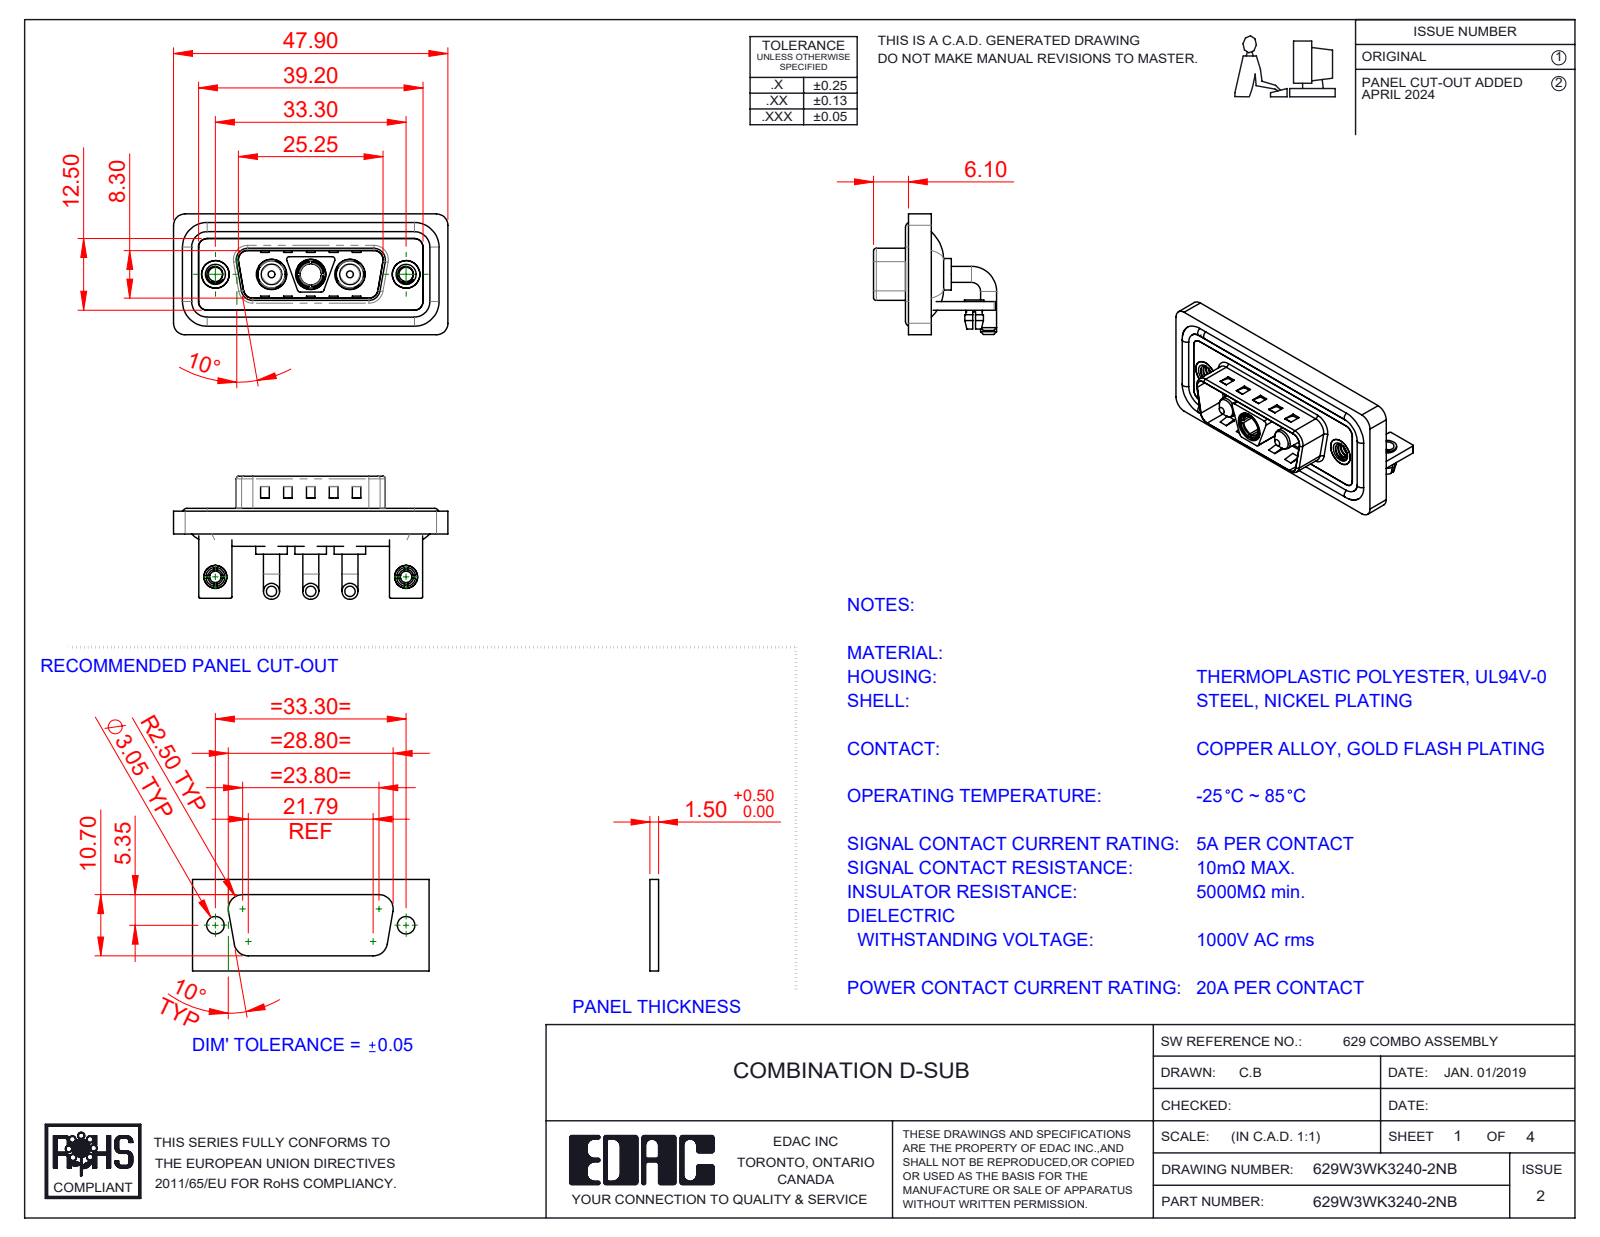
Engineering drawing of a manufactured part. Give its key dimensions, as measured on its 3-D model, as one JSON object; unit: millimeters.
{"part_name": "629Combo Board Lock; Power Pin_20A RA; Power Socket_20A RA; 629Combo Shell Rear_15 Contacts (+6 more)", "step_written_by": "SolidWorks 2023 (CONFIG_CONTROL_DESIGN)", "units": "millimeters", "bodies": {"solids": 17, "faces": 751, "planar": 299, "cylindrical": 306, "other": 146}, "overall_size": [47.9, 21.5, 21.1], "volume_mm3": 6193, "surface_area_mm2": 10214, "round_holes": [[2.5, 4], [4.85, 3], [5.3, 3], [2, 2], [3.2, 2], [4, 2], [4.8, 2], [5, 2], [3.7, 1]], "round_bosses_or_shafts": [[2.8, 6], [1.6, 4], [5.5, 3], [5.2, 3], [4.75, 3], [3.75, 3], [4.9, 2], [4, 2]], "partial_cylinders_radius": [[2, 21], [1.5, 18], [0.25, 16], [0.5, 13], [1.6, 8], [0.6, 4], [0.65, 4], [0.9, 4]], "face_to_face_distances": [0.4, 1.5, 0.8, 2.9, 1.1, 2.1, 3.7, 1.6, 1.2, 4.5], "hole_center_spacings": [6.85, 9.8, 16.65, 23.5, 33.3, 13.7]}
